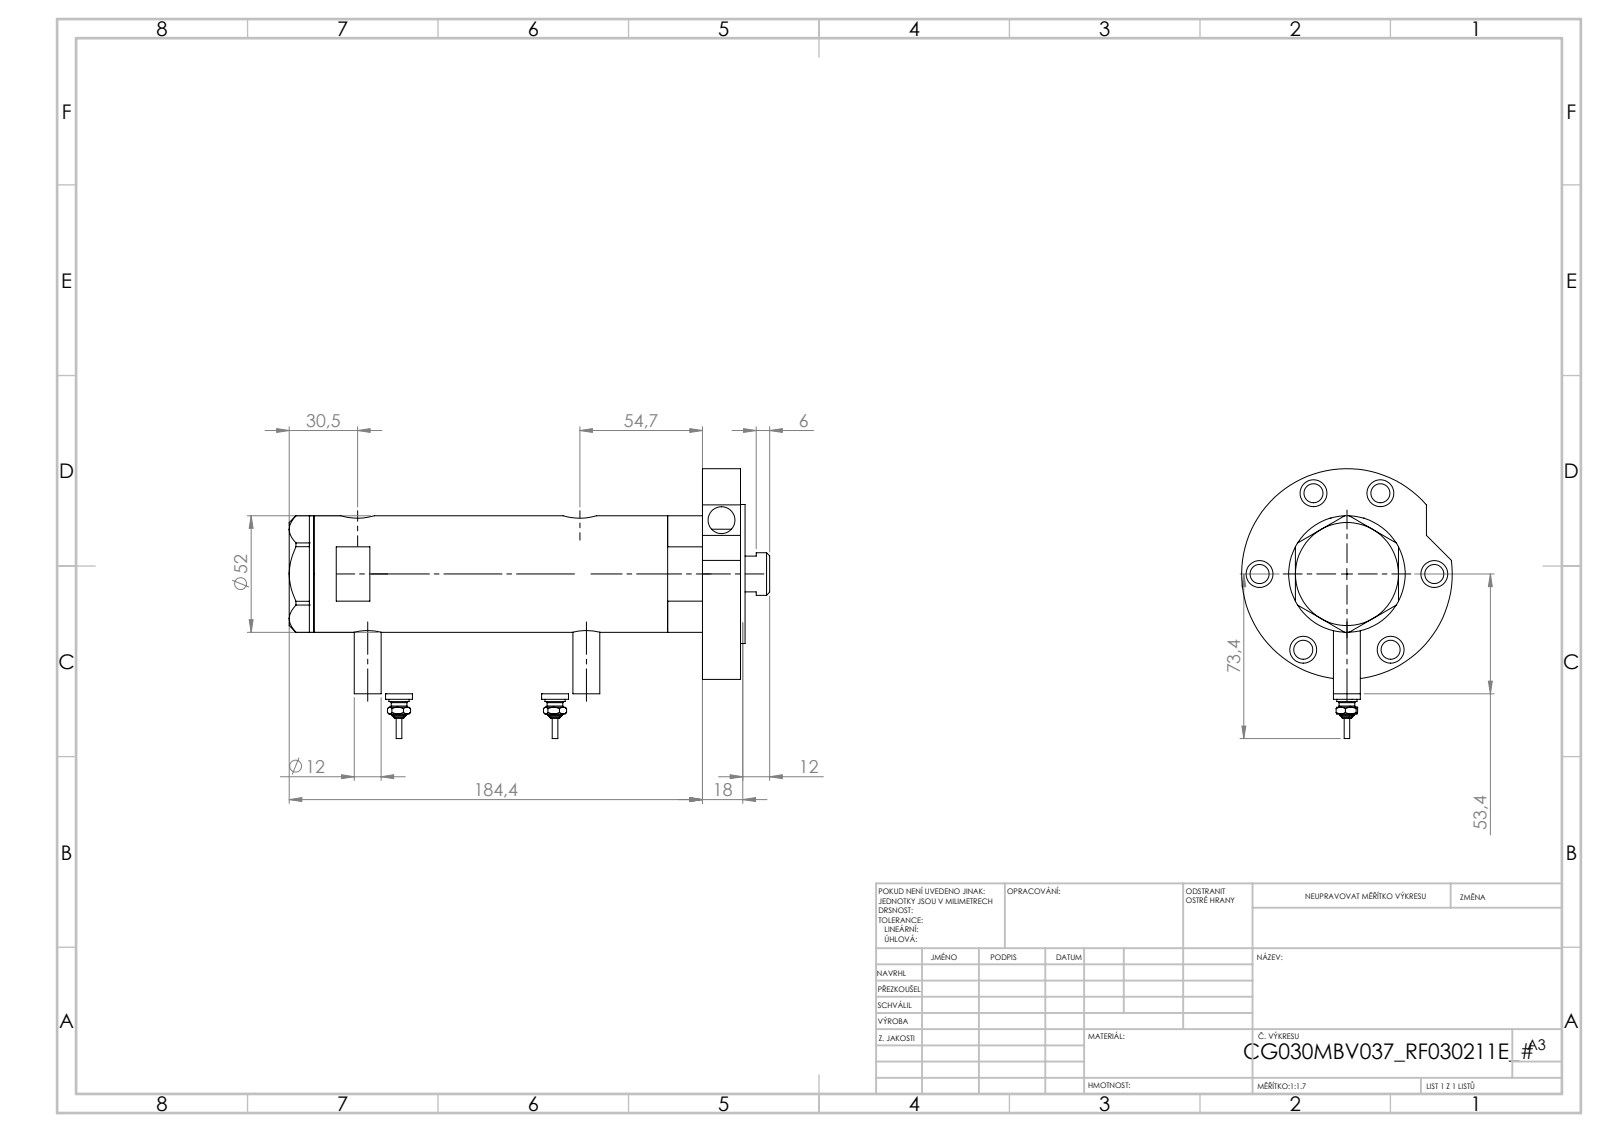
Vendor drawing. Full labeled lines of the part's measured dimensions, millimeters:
Part name (STEP PRODUCT): V270CG_SWITCH; V270CG_VC; V270CG_BACK; V270CG_FRONT (+2 more)
STEP written by: SolidWorks 2019 (CONFIG_CONTROL_DESIGN)
Units: millimetres
Bodies: 7 solids, 290 faces (106 planar, 110 cylindrical, 74 other)
Overall size (bounding box): 186.02 × 105.3 × 94
Volume: 416 234 mm³ · Surface area: 102 674 mm²
Round holes (diameter × count): ⌀12 ×7, ⌀8.5 ×6, ⌀5 ×2, ⌀9.73 ×2, ⌀12.5 ×2, ⌀15 ×2, ⌀6.5 ×1, ⌀20 ×1, ⌀21.5 ×1, ⌀30 ×1, ⌀33 ×1, ⌀40 ×1
Round bosses / shafts (diameter × count): ⌀12 ×3, ⌀9 ×2, ⌀7 ×2, ⌀4.34 ×2, ⌀2.4 ×2, ⌀94 ×1, ⌀62 ×1, ⌀52 ×1
Main face-to-face distances: 17, 142.46, 159.46, 51.9, 2, 161.46, 90.56, 68.9, 70.9, 19
Hole centre spacings: 39, 2.9, 4.5, 43.34, 63.75, 64.85, 66.65, 67.55
